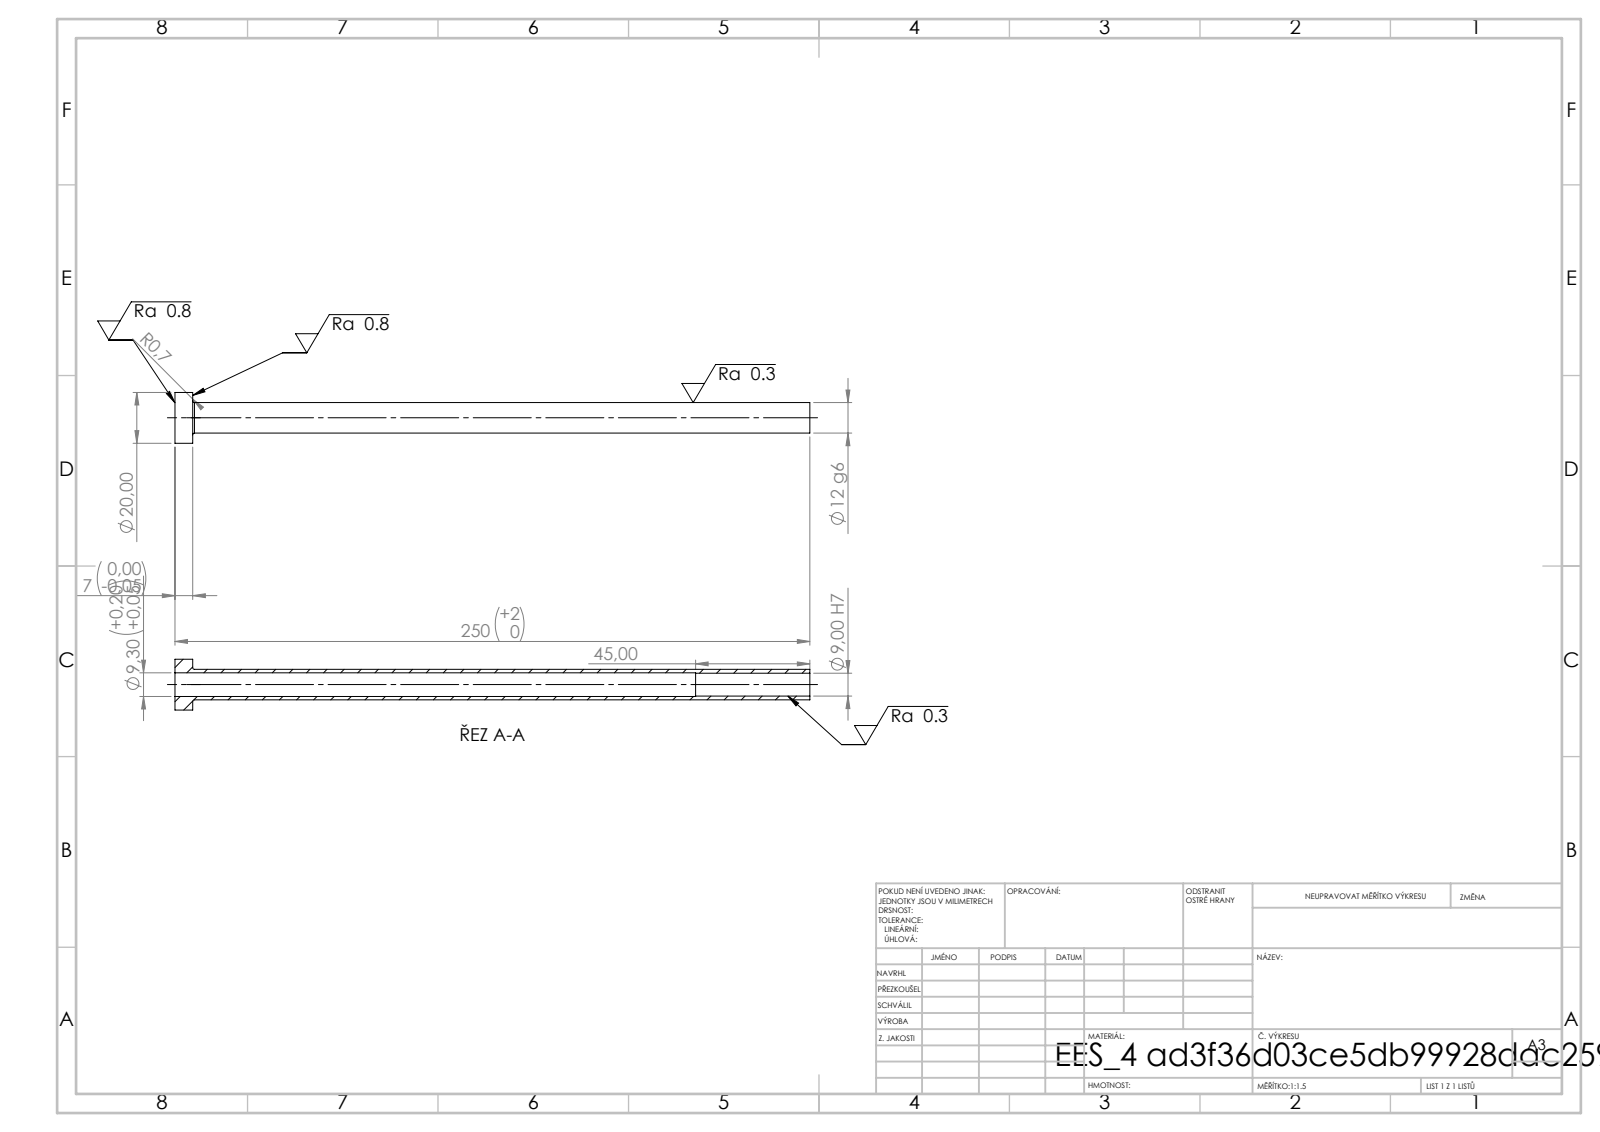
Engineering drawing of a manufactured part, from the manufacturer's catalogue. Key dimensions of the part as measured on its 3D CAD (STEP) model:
STEP written by: SolidWorks 2019 (CONFIG_CONTROL_DESIGN)
Units: millimetres
Bodies: 1 solid, 14 faces (4 planar, 8 cylindrical, 2 other)
Overall size (bounding box): 250 × 20 × 20
Volume: 12 898 mm³ · Surface area: 17 352 mm²
Round holes (diameter × count): ⌀9 ×1, ⌀9.3 ×1
Round bosses / shafts (diameter × count): ⌀20 ×1, ⌀12 ×1
Main face-to-face distances: 7, 250, 243, 205, 198, 45
